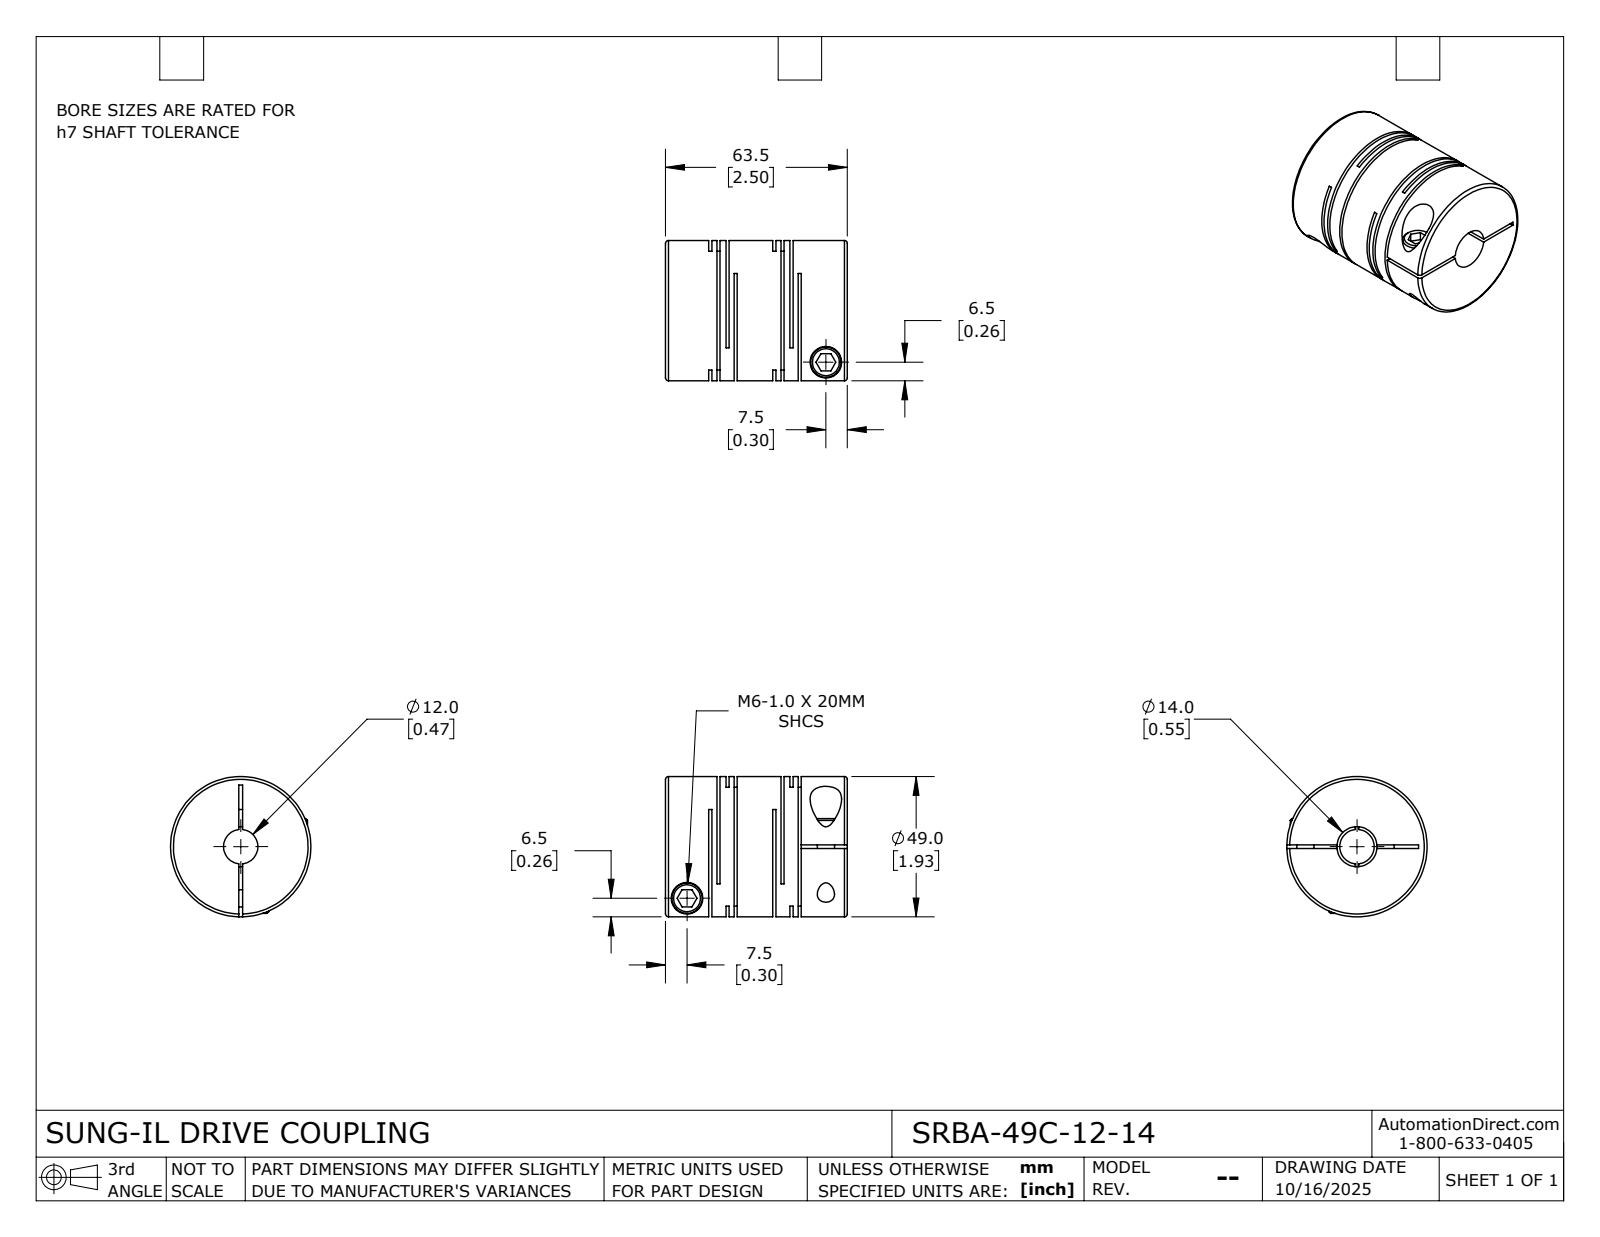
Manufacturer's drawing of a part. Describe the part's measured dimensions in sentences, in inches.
The part is named "SRBA-49C-12-14". Its 3-D file was written by "SolidWorks 2024 (CONFIG_CONTROL_DESIGN)". It is 1 solid with 115 faces: 60 planar, 42 cylindrical and 13 other. Overall it measures 2.5 by 1.929 by 1.929 inches. Its volume is 5.816 cubic inches and its surface area 62.33 square inches. Round holes: 2 of diameter 0.236, 2 of diameter 0.433, 1 of diameter 0.472, 1 of diameter 0.551. Round bosses or shafts: 2 of diameter 0.417, 1 of diameter 1.929. The main face-to-face distances are 0.236, 0.043, 0.88, 0.112, 0.837, 0.124, 0.069, 0.193, 0.768, 0.644.
